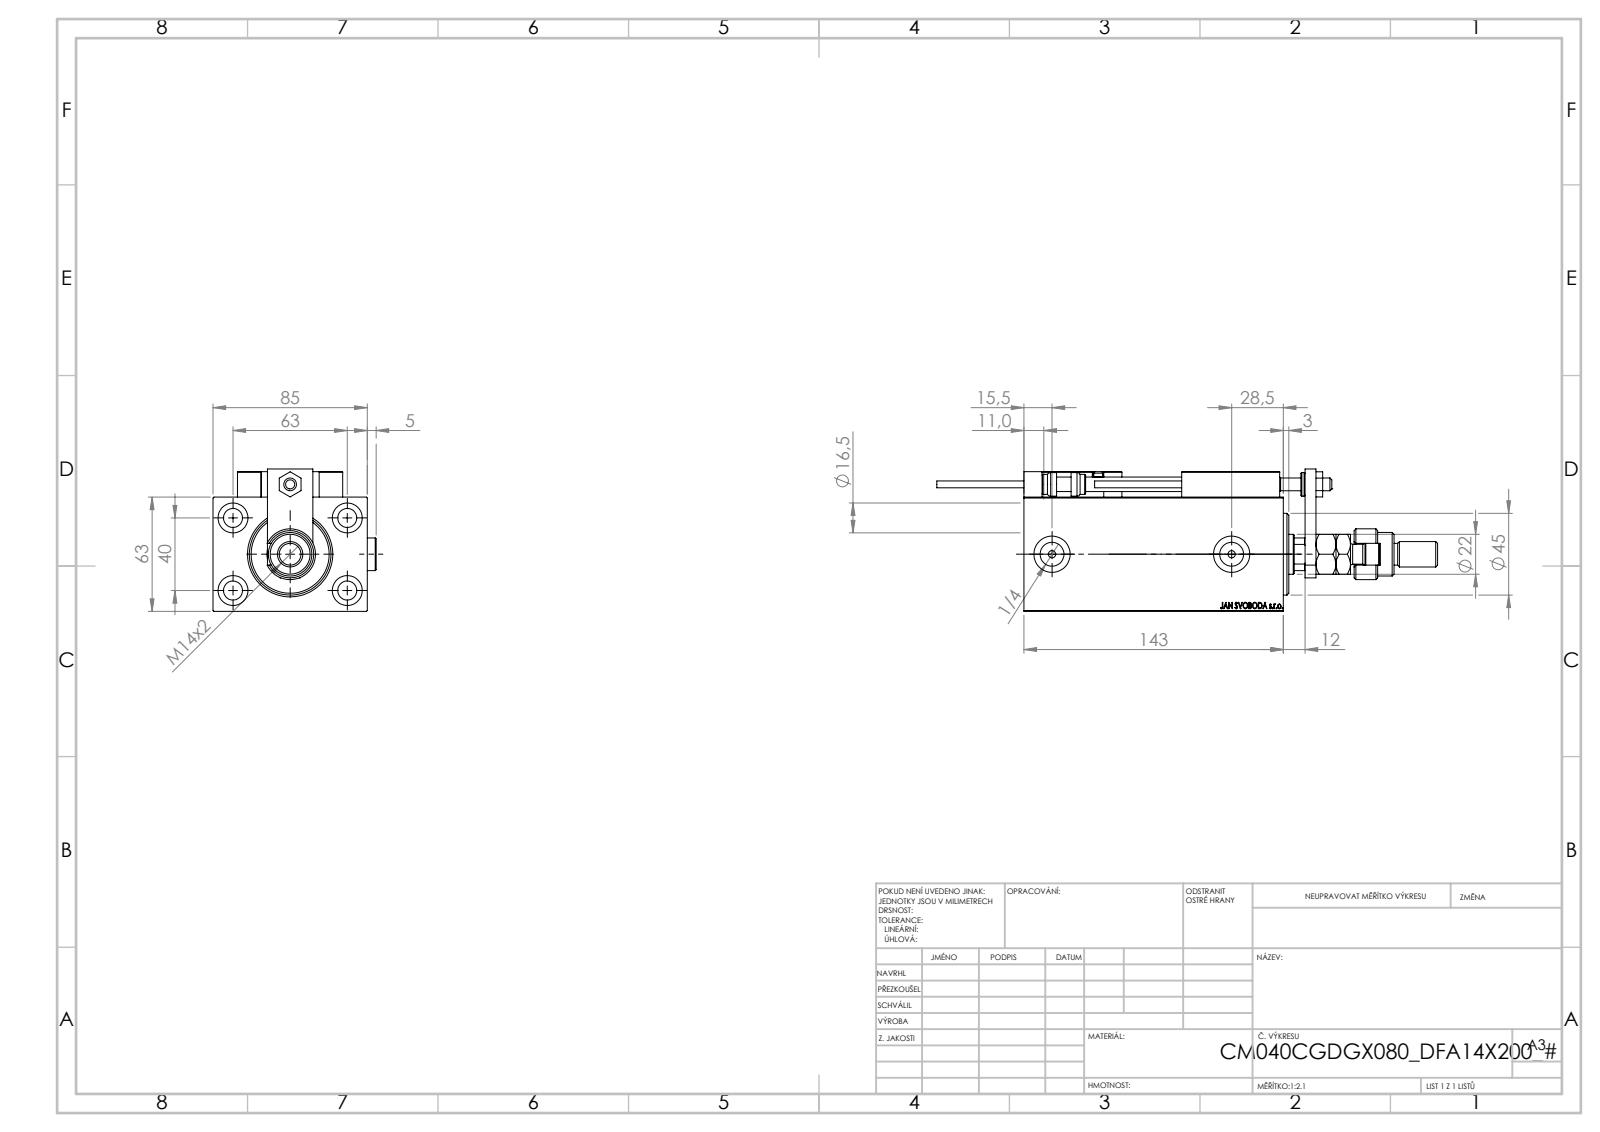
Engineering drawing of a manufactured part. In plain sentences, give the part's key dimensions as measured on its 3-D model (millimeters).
The part is named "ALLEN BOLT D8; SWITCH X; KONCOVKA; MAGNET (+7 more)". Its 3-D file was written by "SolidWorks 2019 (CONFIG_CONTROL_DESIGN)". It is 27 solids with 1421 faces: 622 planar, 217 cylindrical and 582 other. Overall it measures 276 by 89.9 by 78.5 millimeters. Its volume is 707 754 cubic millimeters and its surface area 148 325 square millimeters. Round holes: 6 of diameter 4, 5 of diameter 8, 5 of diameter 16.5, 4 of diameter 3.2, 4 of diameter 10.5, 2 of diameter 5, 2 of diameter 13.16, 2 of diameter 20, 1 of diameter 7, 1 of diameter 12.5, 1 of diameter 22, 1 of diameter 25.5. Round bosses or shafts: 3 of diameter 18, 2 of diameter 11, 2 of diameter 5, 2 of diameter 3.8, 1 of diameter 28, 1 of diameter 24, 1 of diameter 14, 1 of diameter 13. Partial cylindrical surfaces (rounded edges, fillets, slot ends): 30 of radius 0.3, 2 of radius 3, 1 of radius 9.75, 1 of radius 10.5. The main face-to-face distances are 63, 85, 12, 131, 143, 14, 77, 30, 18, 6. The hole center spacings are 37.31, 11.37, 20, 29.59, 29.69, 36.06, 36.53, 40.
